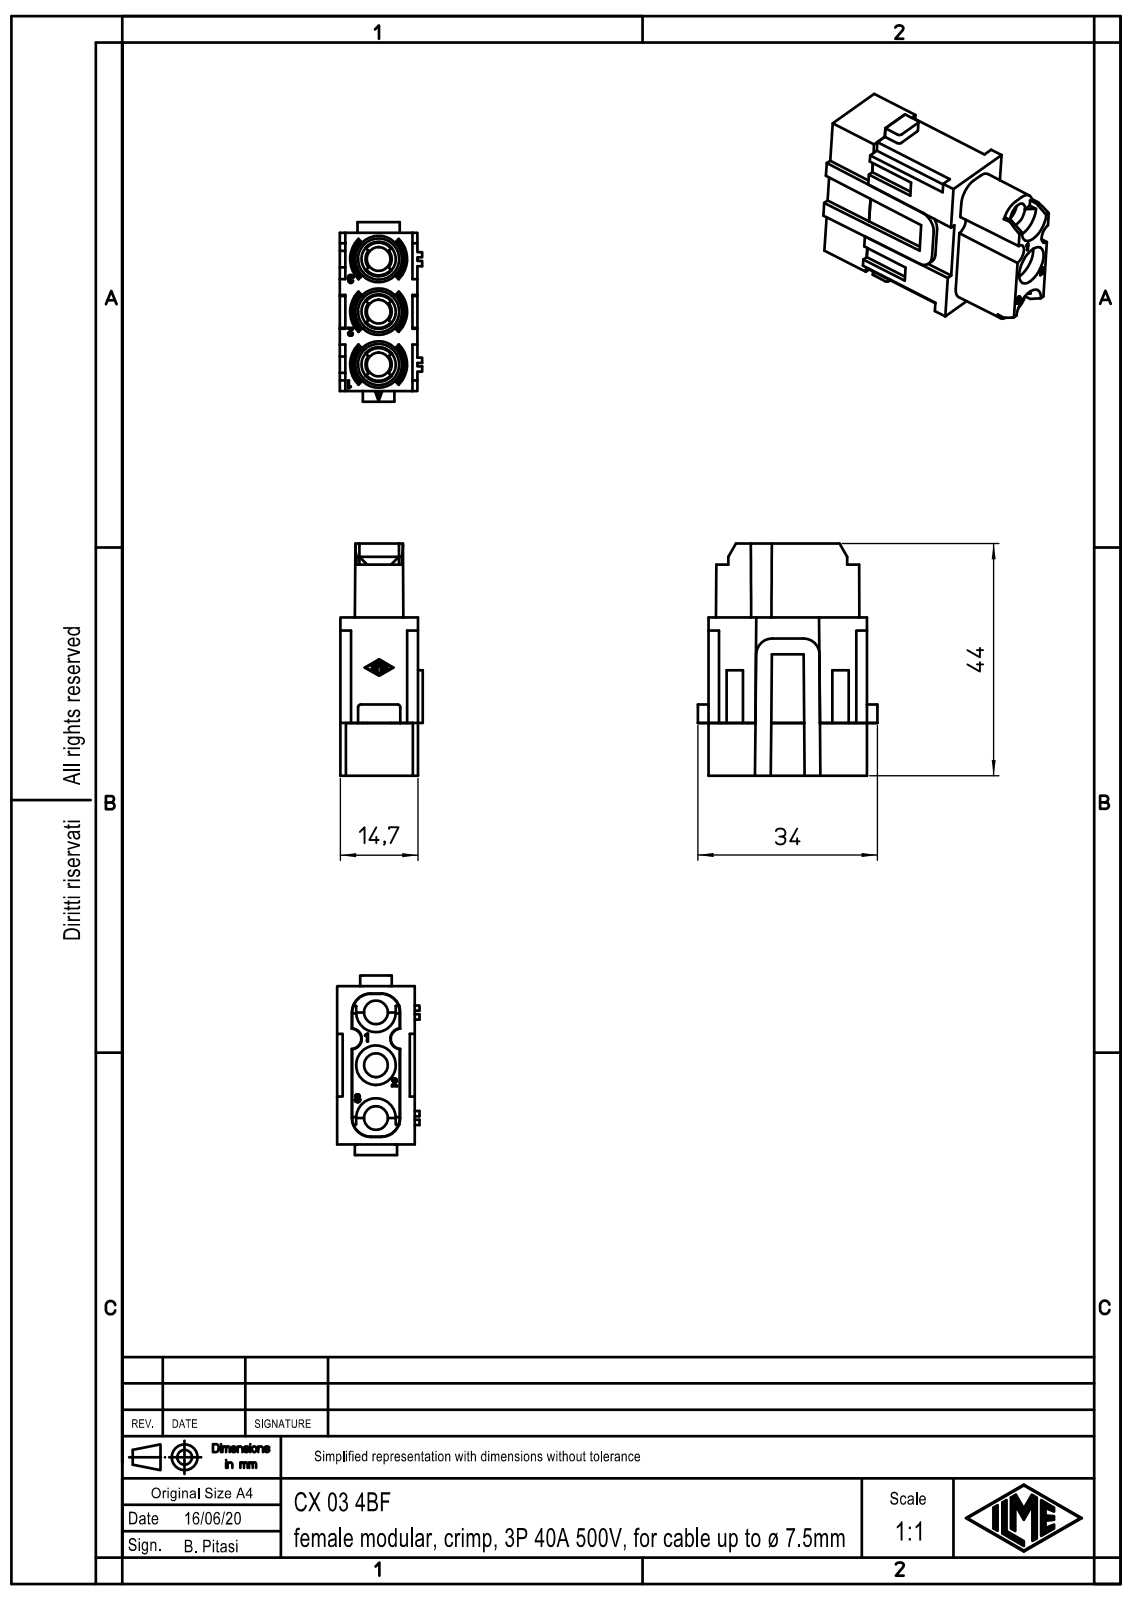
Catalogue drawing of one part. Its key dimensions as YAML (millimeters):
part_name: "CX 03 4BF"
step_written_by: "Creo Elements/Direct Modeling 20.1B 02-Apr-2019 (C) Parametric Technology GmbH (AUTOMOTIVE_DESIGN)"
units: millimeters
bodies: {solids: 1, faces: 278, planar: 244, cylindrical: 28, other: 6}
overall_size: [44.11, 34, 15.7]
volume: 11125
surface_area: 7344
round_holes:
  - {diameter: 5, count: 3}
  - {diameter: 6, count: 3}
  - {diameter: 8, count: 1}
partial_cylinders:
  - {radius: 0.5, count: 2}
  - {radius: 2, count: 2}
  - {radius: 3.5, count: 2}
  - {radius: 4, count: 2}
  - {radius: 4.5, count: 2}
face_to_face_distances: [1.35, 13.35, 12, 1.5, 10.5, 9, 2, 14.7, 30, 2.85]
hole_center_spacings: [10, 20]
